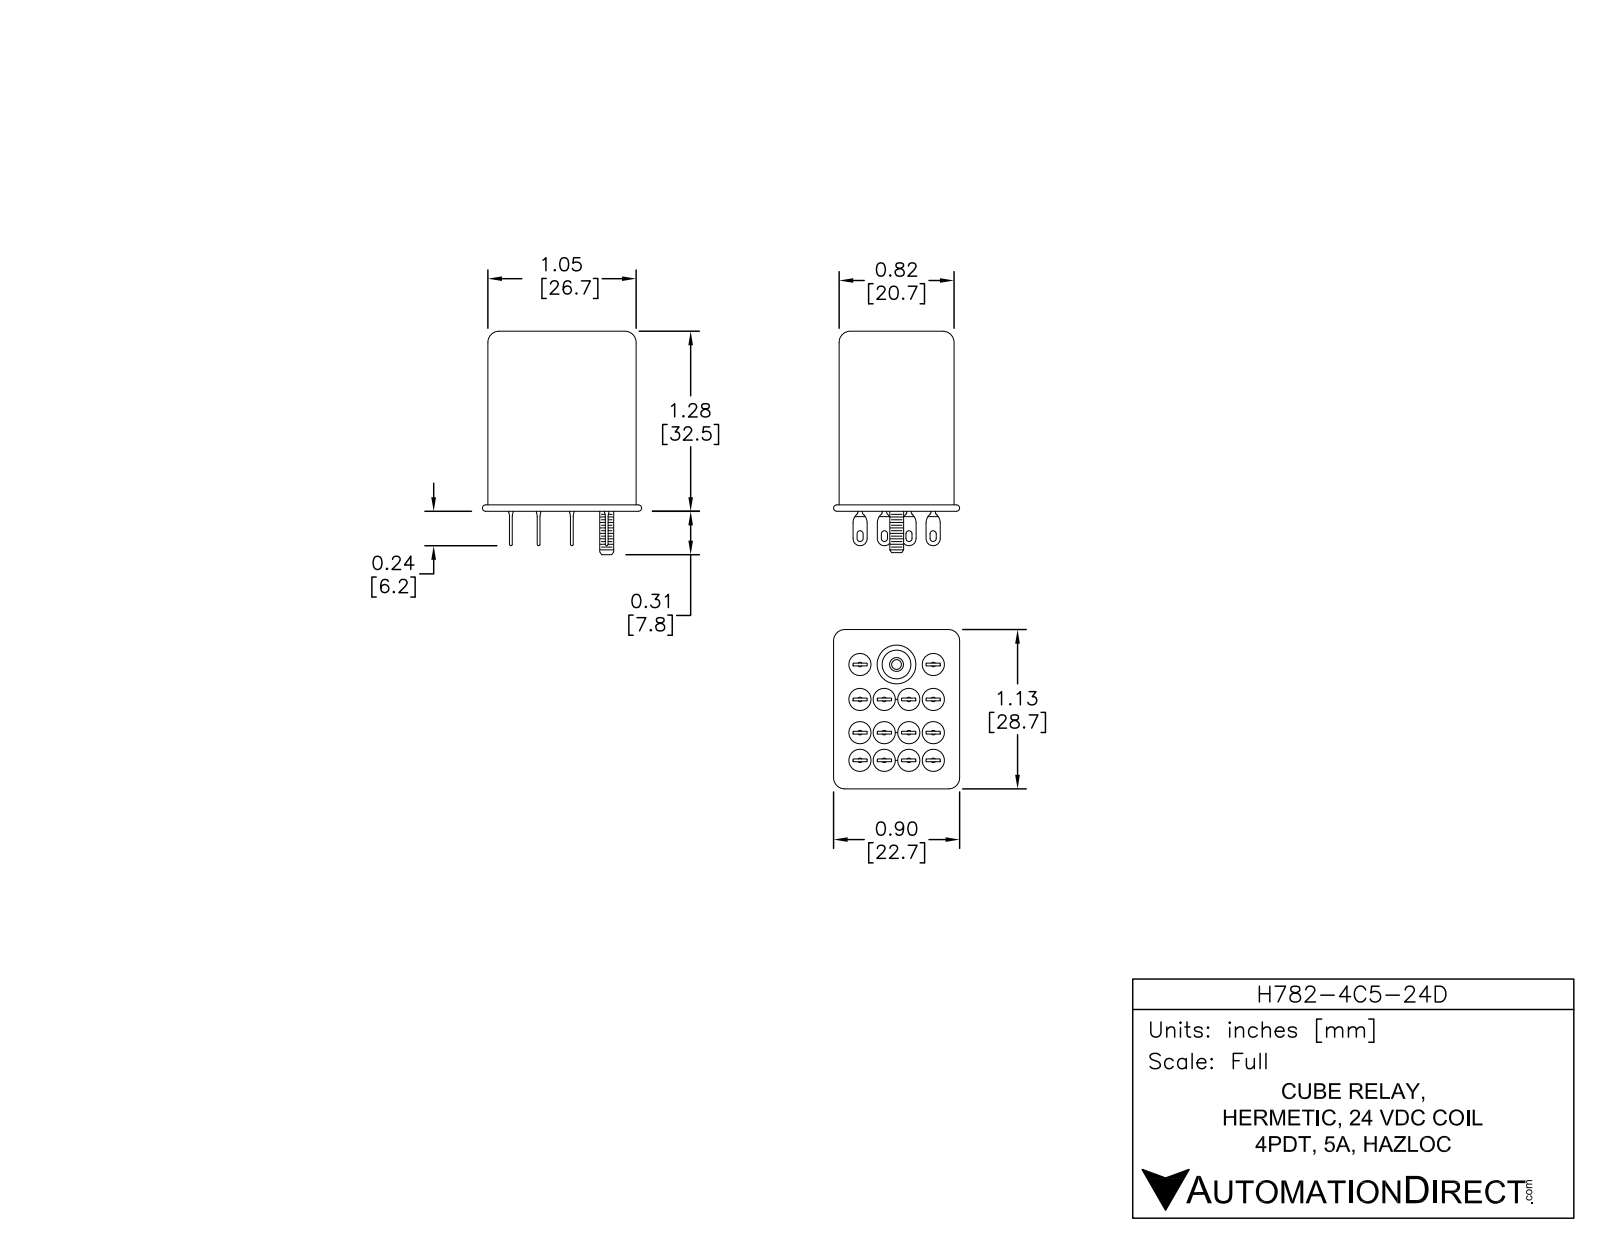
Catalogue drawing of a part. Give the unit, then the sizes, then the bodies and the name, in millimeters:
Units: millimetres
Overall size (bounding box): 35.12 × 28.8 × 22.9
Round holes (diameter × count): ⌀6 ×1
Round bosses / shafts (diameter × count): ⌀3.15 ×14, ⌀2.4 ×1
Partial cylindrical surfaces — rounded edges, fillets, slot ends (radius × count): R0.1 ×56, R0.5 ×36, R0.2 ×8, R2 ×4
Main face-to-face distances: 20.5, 27.6, 26.5, 27.62, 5.2, 0.4, 10.4, 10, 4.8, 5.6
Volume: 15 264 mm³ · Surface area: 4 133 mm²
Bodies: 2 solids, 408 faces (186 planar, 178 cylindrical, 44 other)
Part name (STEP PRODUCT): H782-4C5-24D
STEP written by: SolidWorks 2013 (AUTOMOTIVE_DESIGN)
